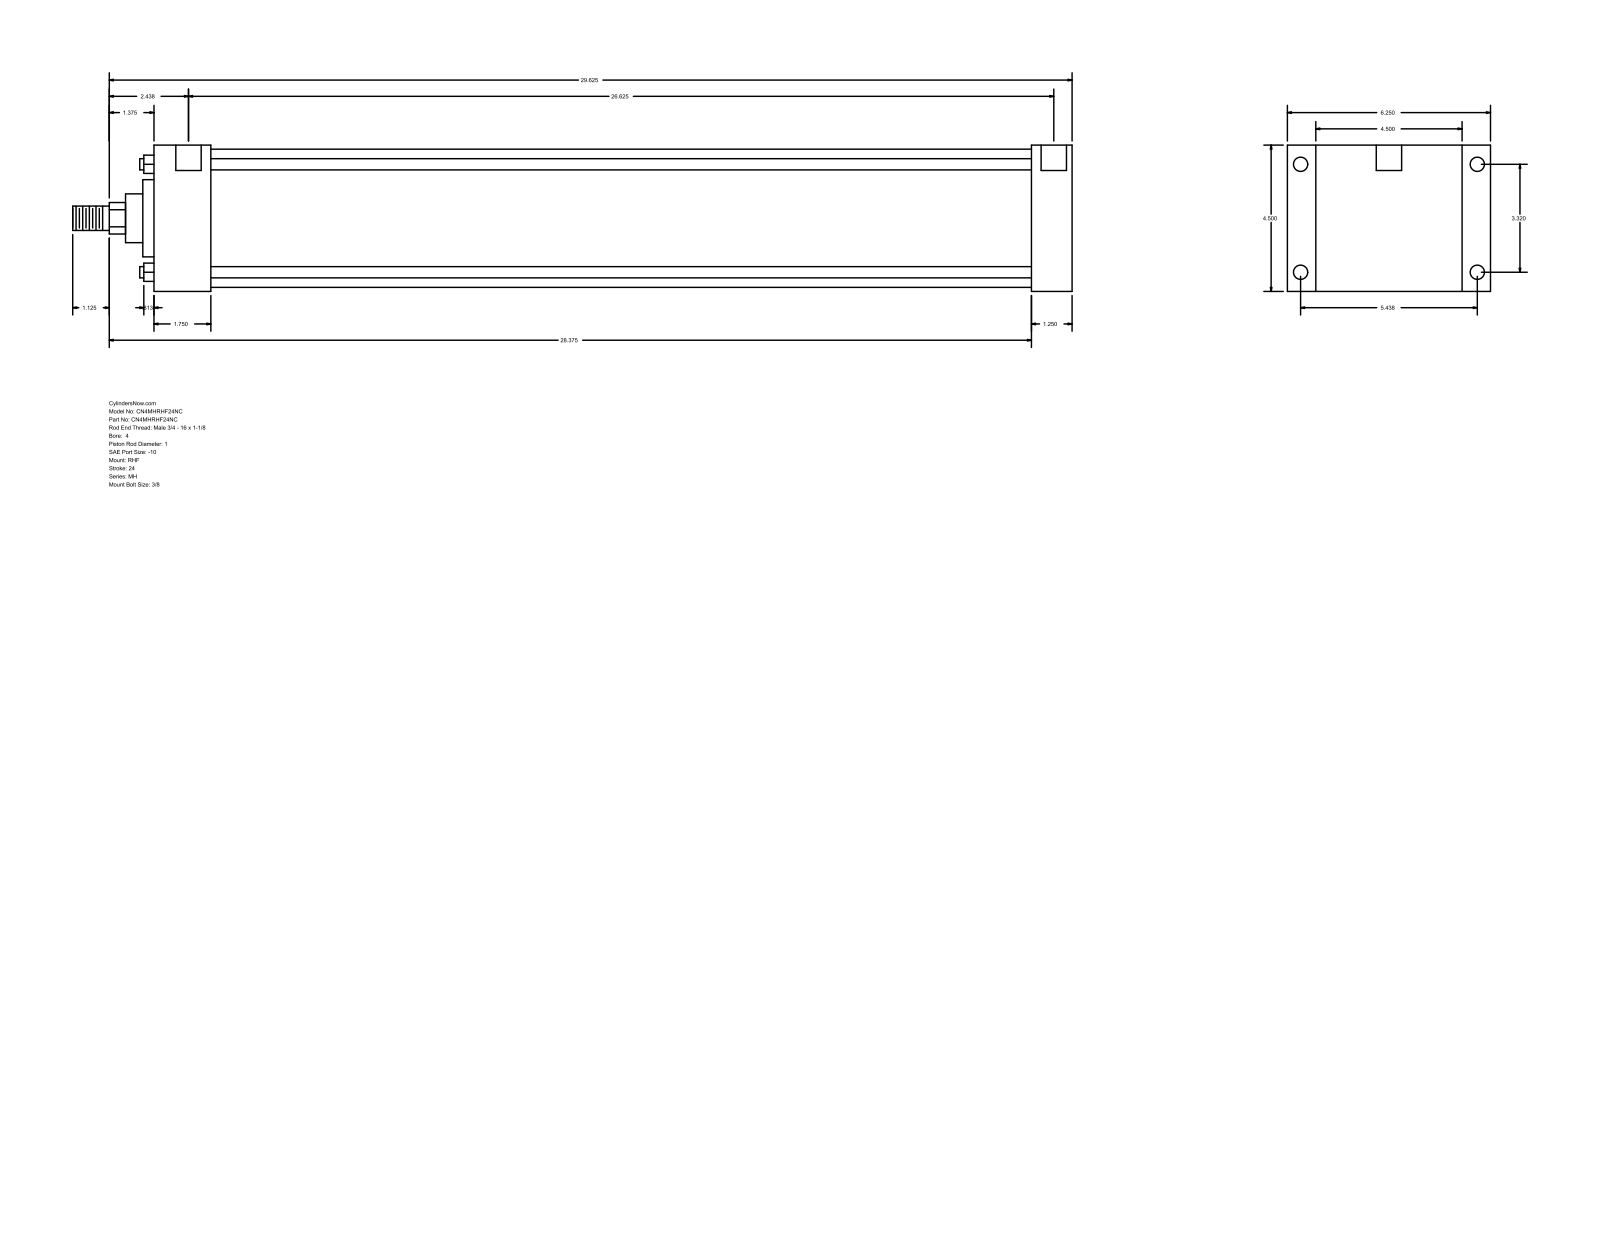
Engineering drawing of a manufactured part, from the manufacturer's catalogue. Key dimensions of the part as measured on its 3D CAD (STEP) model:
Part name (STEP PRODUCT): MH_RHF__0400_1
STEP written by: GSSL Pune (CONFIG_CONTROL_DESIGN)
Units: millimetres
Bodies: 0 solids, 90 faces (61 planar, 29 cylindrical, 0 other)
Overall size (bounding box): 781.05 × 158.75 × 114.3
Round holes (diameter × count): ⌀8.73 ×4, ⌀11.13 ×4, ⌀19.84 ×2
Round bosses / shafts (diameter × count): ⌀8.76 ×4, ⌀107.95 ×1, ⌀60.33 ×1, ⌀38.1 ×1, ⌀25.4 ×1, ⌀19.05 ×1
Partial cylindrical surfaces — rounded edges, fillets, slot ends (radius × count): R12.29 ×1
Main face-to-face distances: 114.3, 717.56, 685.81, 31.75, 22.23, 136.53, 44.46, 641.35, 673.1, 158.76
Hole centre spacings: 1.58, 84.32, 138.12, 161.82, 677.86, 679.44, 676.28
